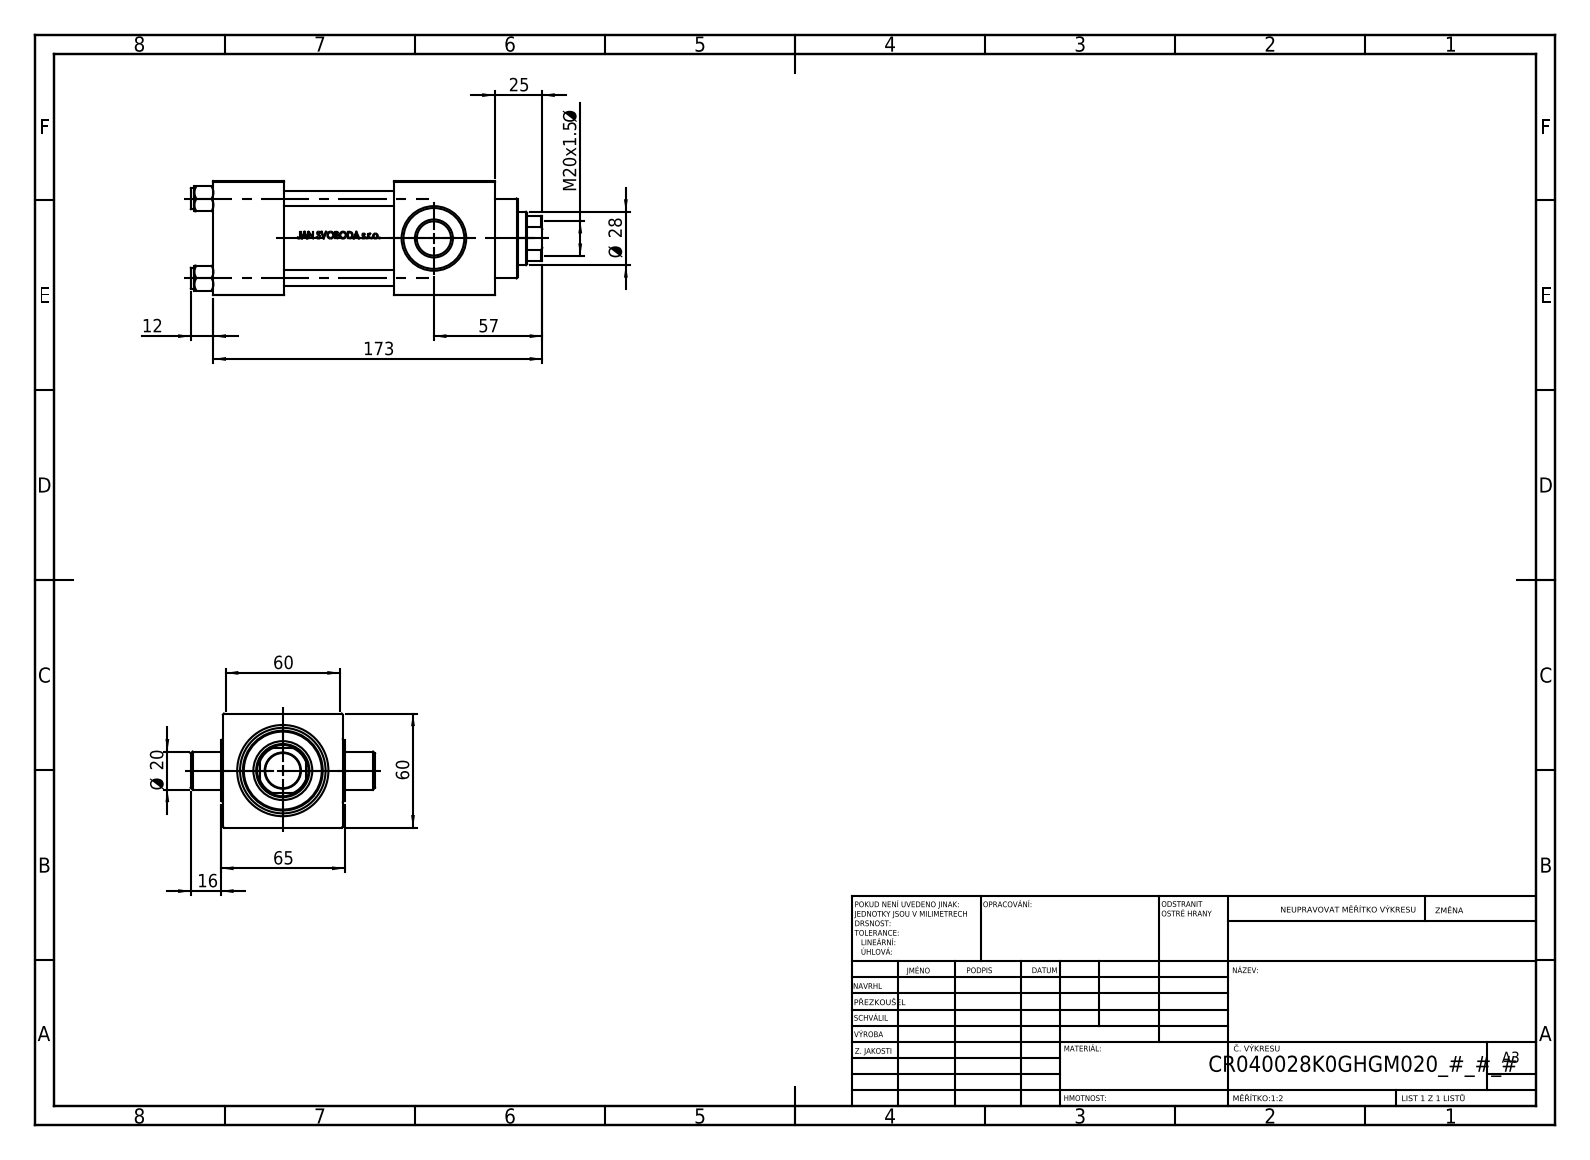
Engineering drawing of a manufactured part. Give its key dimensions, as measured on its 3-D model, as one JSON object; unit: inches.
{"part_name": "V215CR_VCP_K; V215CR_K_TYCINKA; V215CR_K_Body; V215_VC_A (+1 more)", "step_written_by": "SolidWorks 2019 (CONFIG_CONTROL_DESIGN)", "units": "inches", "bodies": {"solids": 11, "faces": 1059, "planar": 427, "cylindrical": 110, "other": 522}, "overall_size": [7.283, 3.819, 2.362], "volume_in3": 27.71, "surface_area_in2": 169.9, "round_holes": [[0.315, 4], [0.276, 1], [0.728, 1], [1.102, 1], [1.22, 1], [1.575, 1], [1.772, 1]], "round_bosses_or_shafts": [[0.433, 4], [1.811, 1], [1.654, 1], [0.787, 1]], "partial_cylinders_radius": [[0.531, 1]], "face_to_face_distances": [2.362, 0.059, 2.421, 1.457, 2.48, 3.74, 2.283, 5.827, 4.37, 2.087], "hole_center_spacings": [1.161, 1.642, 2.322]}
